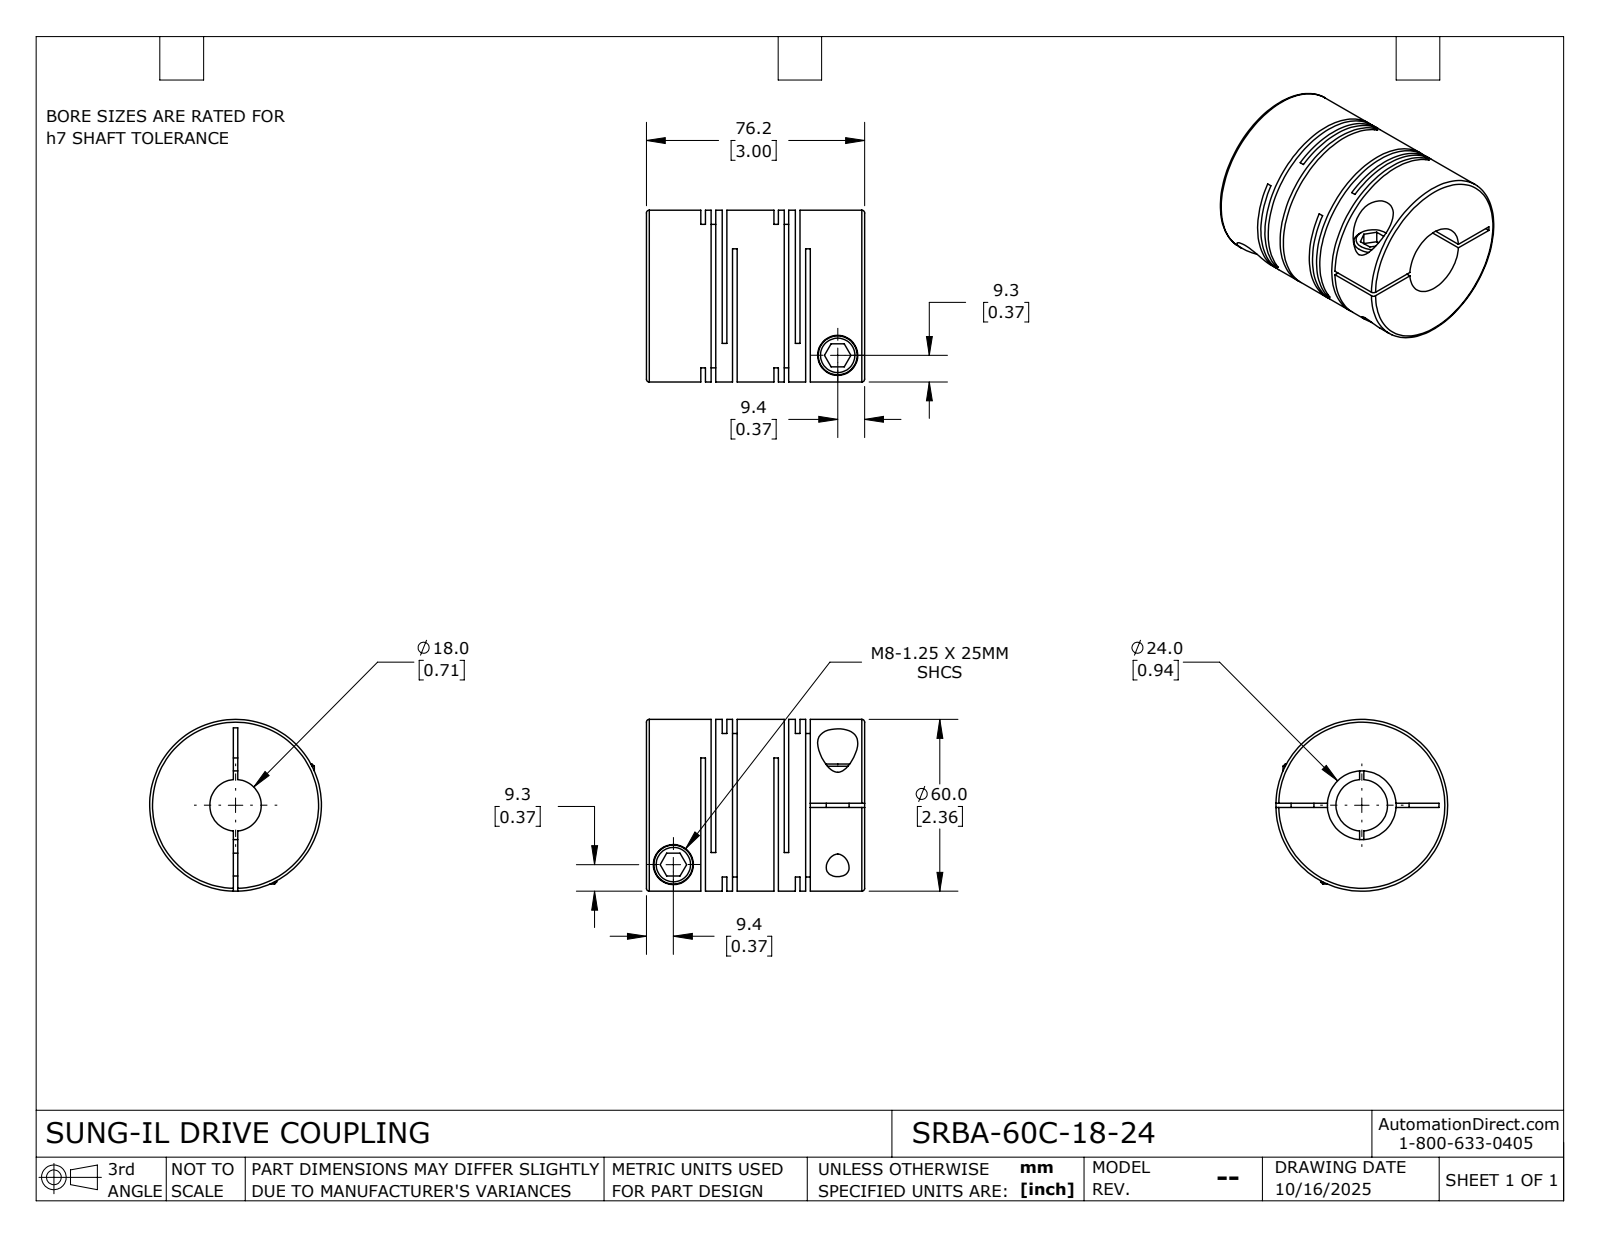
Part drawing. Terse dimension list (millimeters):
name: SRBA-60C-18-24
written by: SolidWorks 2024 (CONFIG_CONTROL_DESIGN)
unit: mm
bodies: 1 solid, 115 faces (60 planar, 42 cylindrical, 13 other)
size: 76.2 × 60 × 60
volume: 155 332 mm³; area: 57 397 mm²
holes: 2× ⌀8, 2× ⌀14, 1× ⌀18, 1× ⌀24
bosses: 2× ⌀13.6, 1× ⌀60
face distances: 1.6, 3.6, 7.5, 25.5, 33, 27.1, 2, 5.9, 23.9, 3.9
